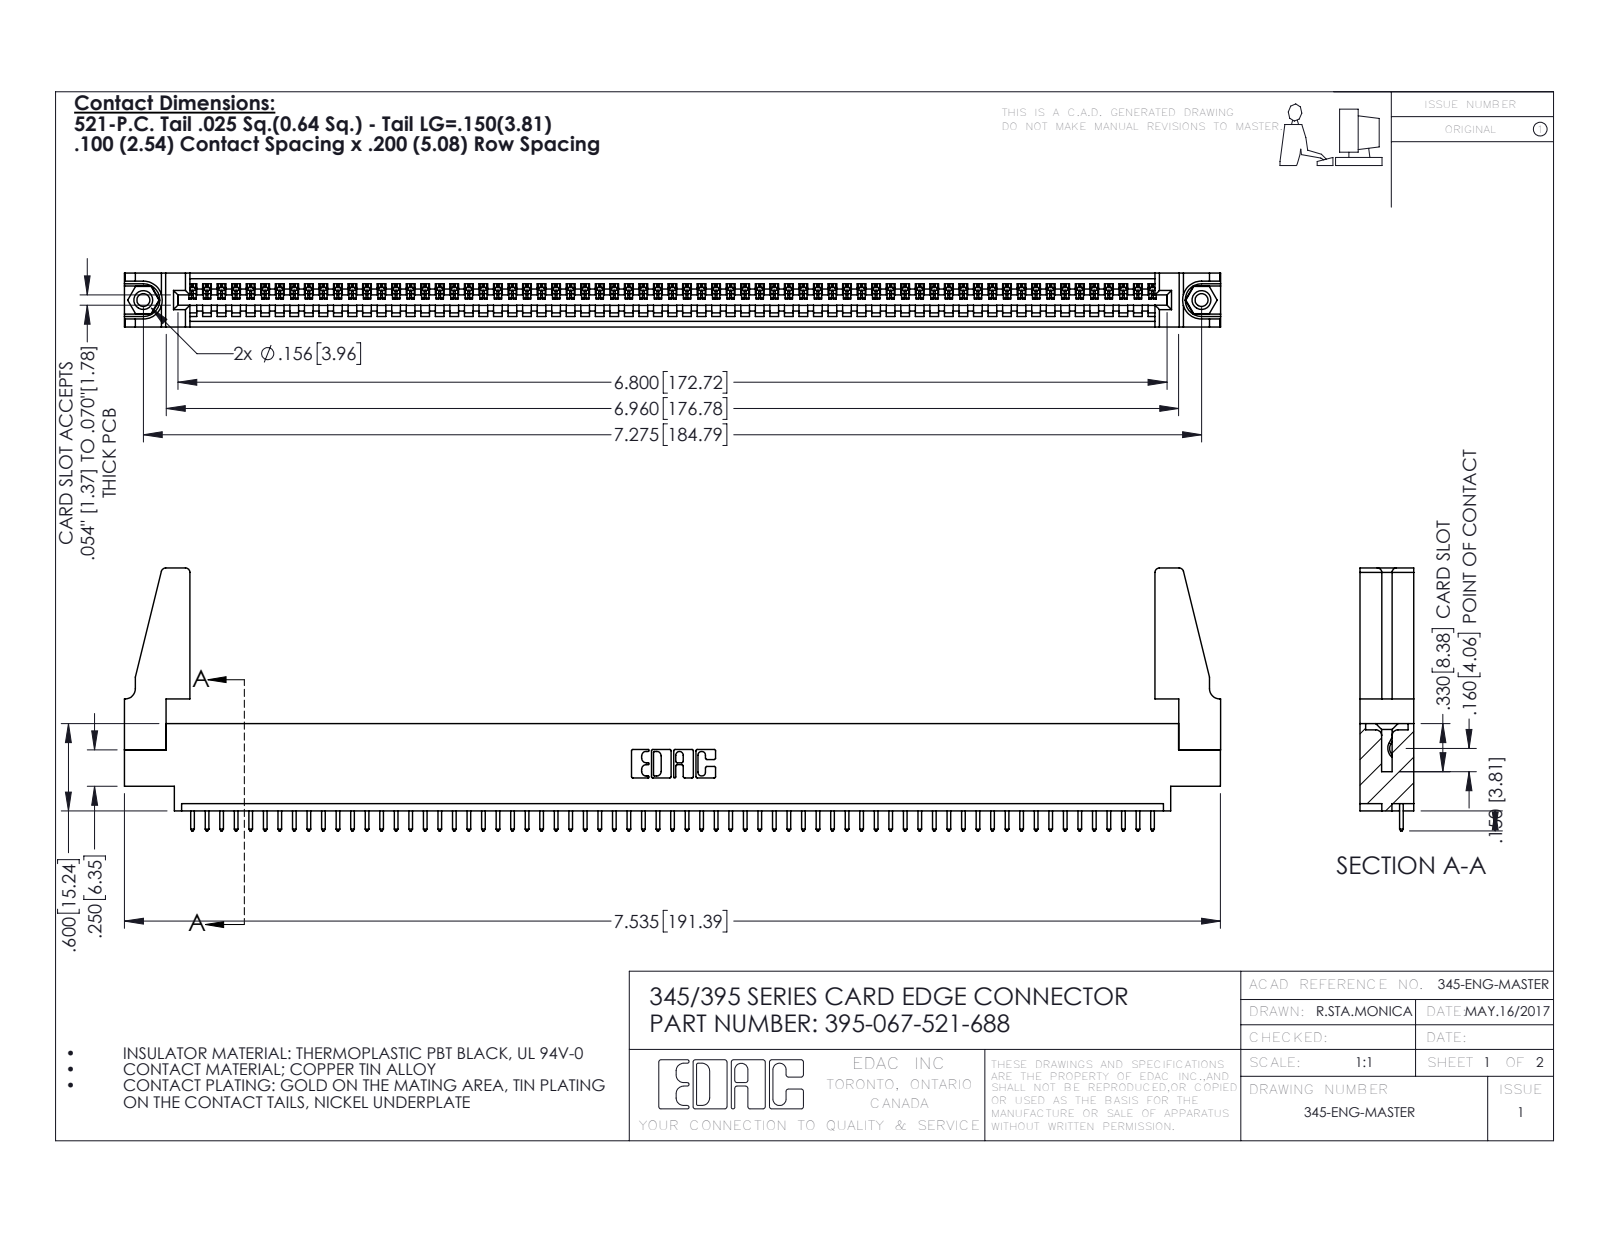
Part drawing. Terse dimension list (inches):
name: 345 Part_0.170 Offset - 0.156 Dia-TH; 395-067-521-688; 345-250-001_345-250-001-102; 345-292-001_345-293-121 (+1 more)
written by: SolidWorks 2016 (CONFIG_CONTROL_DESIGN)
unit: in
bodies: 72 solids, 4140 faces (2836 planar, 1288 cylindrical, 16 other)
size: 7.536 × 1.807 × 0.37
volume: 1.302 in³; area: 41.66 in²
holes: 2× ⌀0.089, 2× ⌀0.125, 2× ⌀0.156, 1× ⌀0.064
bosses: 2× ⌀0.155
rounds: 134× R0.006, 134× R0.01, 22× R0.01, 8× R0.03, 6× R0.007, 6× R0.031, 3× R0.026, 2× R0.031
face distances: 0.072, 0.298, 0.37, 0.098, 0.272, 0.025, 0.2, 0.225, 0.175, 0.149
hole spacings: 0.27, 7.039, 7.275
